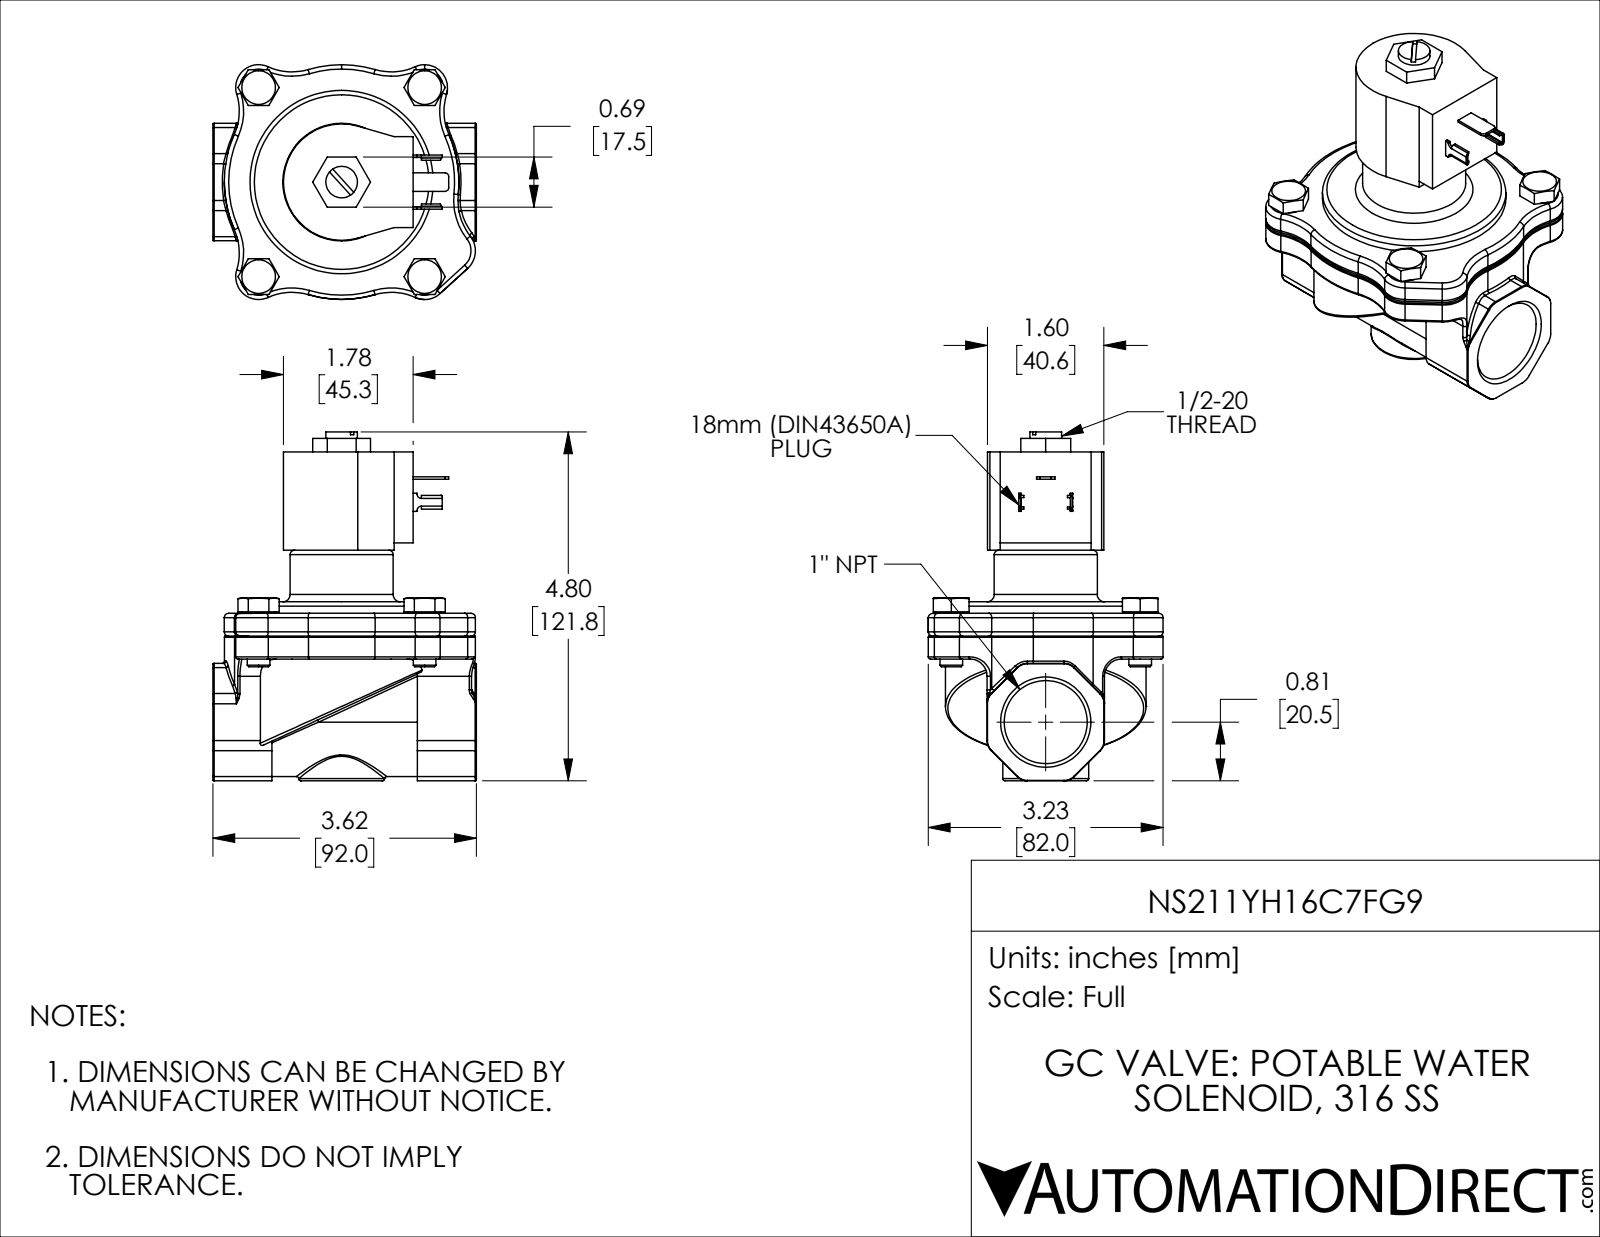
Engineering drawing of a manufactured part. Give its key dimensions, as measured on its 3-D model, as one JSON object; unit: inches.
{"part_name": "NS211YH16C7FG9", "step_written_by": "SolidWorks 2024 (CONFIG_CONTROL_DESIGN)", "units": "inches", "bodies": {"solids": 9, "faces": 582, "planar": 151, "cylindrical": 223, "other": 208}, "overall_size": [4.795, 3.622, 3.228], "volume_in3": 18.11, "surface_area_in2": 100.5, "round_holes": [[0.25, 4], [0.313, 4], [0.125, 1], [0.236, 1], [0.434, 1], [0.504, 1], [0.949, 1], [1.141, 1], [3, 1]], "round_bosses_or_shafts": [[0.45, 4], [0.313, 4], [2.65, 1], [2.52, 1], [1.417, 1], [1.181, 1]], "partial_cylinders_radius": [[0.031, 26], [0.787, 16], [0.197, 8], [0.315, 6], [0.006, 4], [0.041, 4], [0.06, 4], [0.05, 2]], "face_to_face_distances": [0.03, 0.345, 0.315, 2.561, 2.531, 2.216, 1.211, 1.181, 0.866, 1.35], "hole_center_spacings": [2.598, 2.283, 3.459, 1.729, 1.73, 1.73, 2.274, 2.282]}
